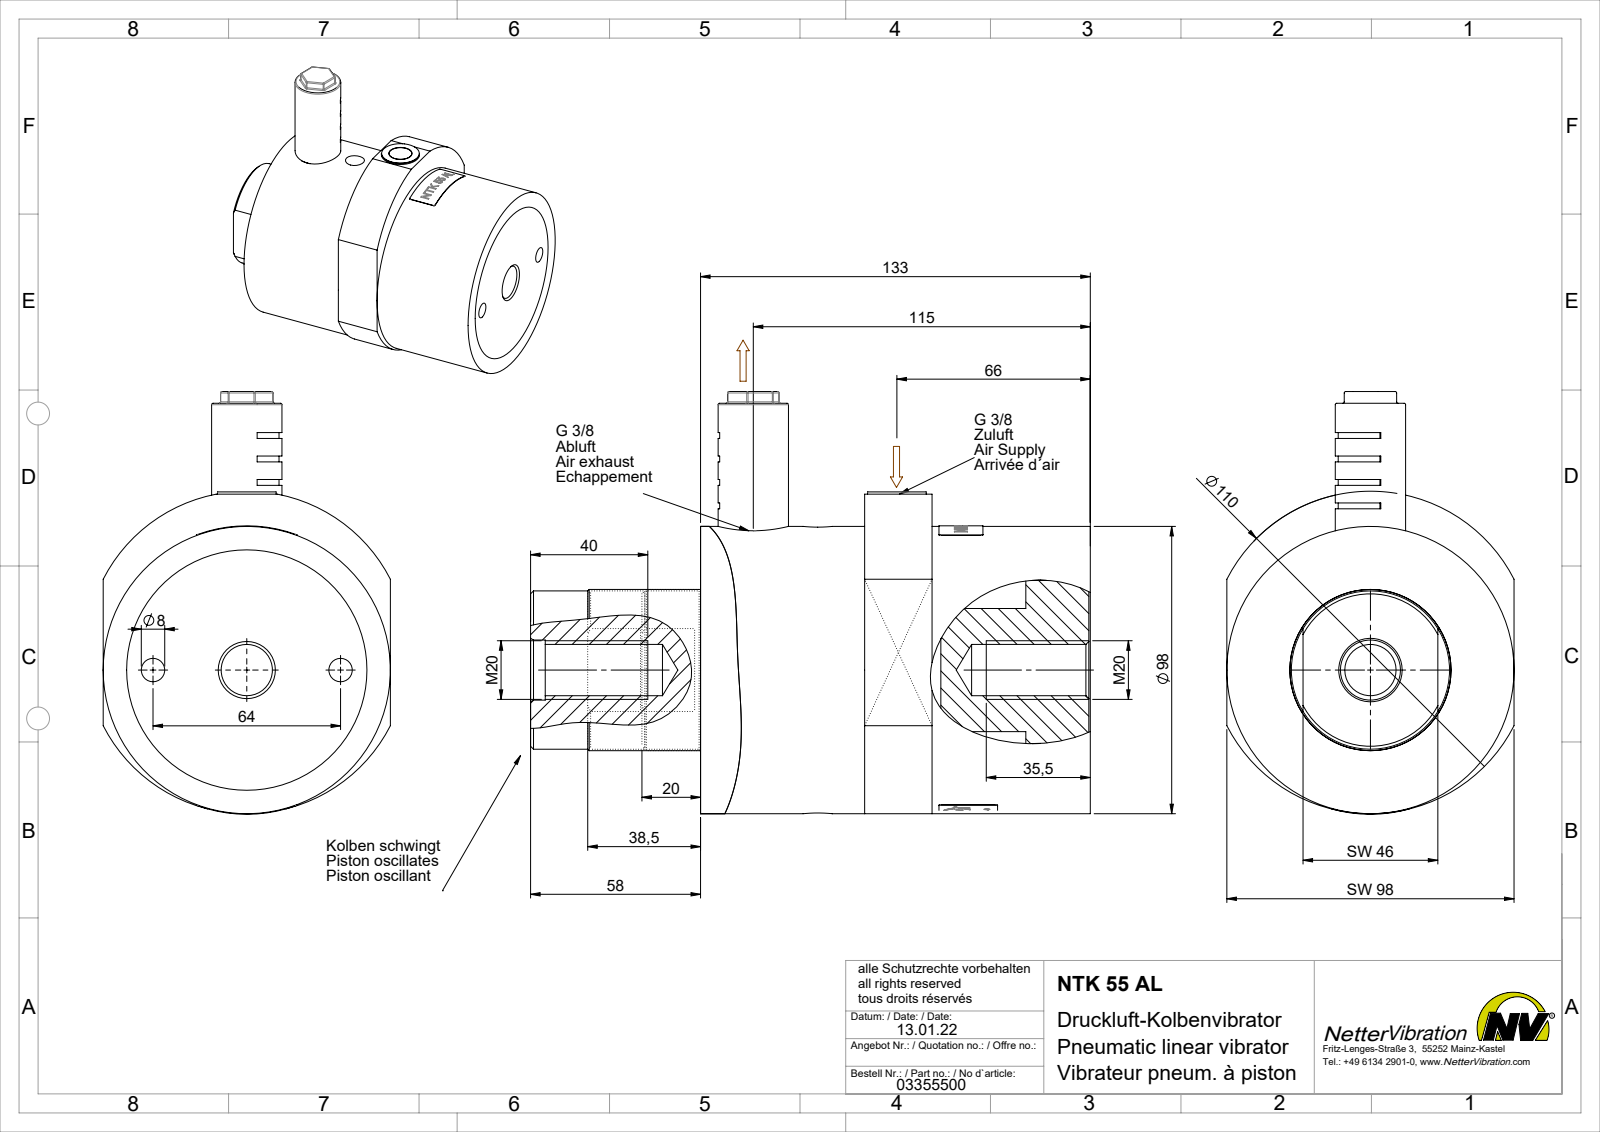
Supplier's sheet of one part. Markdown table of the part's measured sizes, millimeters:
| quantity | value |
| --- | --- |
| part name | NTK 55 AL #03355500 |
| STEP written by | SolidWorks 2015 (AUTOMOTIVE_DESIGN) |
| units | millimeters |
| bodies | 6 solids, 280 faces (58 planar, 175 cylindrical, 47 other) |
| overall size | 171 × 144.2 × 98 |
| volume | 954 283 mm³ |
| surface area | 130 941 mm² |
| round holes (diameter × count) | 8 × 2, 14.95 × 2, 5 × 1, 10 × 1, 17.5 × 1, 20.5 × 1, 55 × 1, 82 × 1 |
| round bosses / shafts (diameter × count) | 98 × 1, 85 × 1, 54 × 1, 42 × 1, 24 × 1, 16.66 × 1 |
| partial cylindrical surfaces (radius × count) | 0.5 × 26, 11 × 1, 49.2 × 1, 55 × 1 |
| main face-to-face distances | 131.5, 117, 110, 21.5, 23, 7, 14.5, 38, 54, 16 |
| hole center spacings | 32, 22, 27, 49, 64 |
